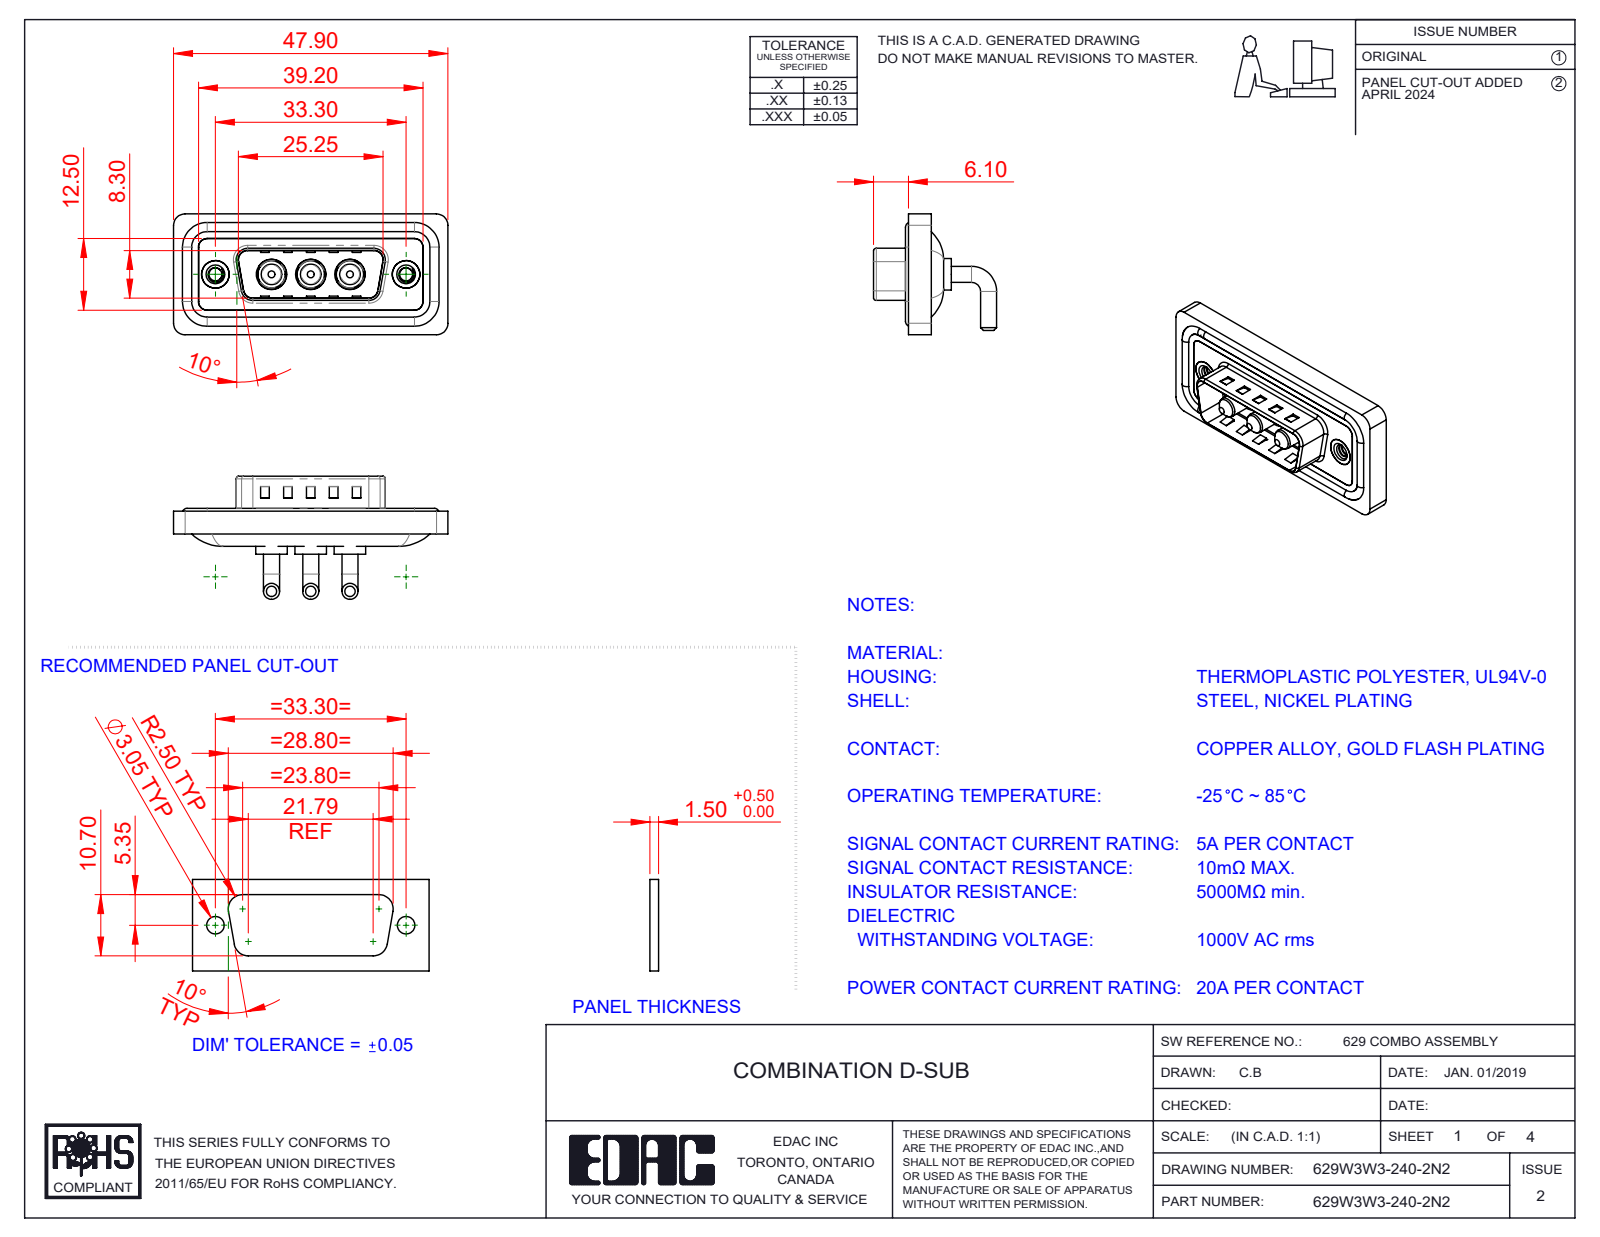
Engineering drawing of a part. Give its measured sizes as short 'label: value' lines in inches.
name: 629Combo Waterproof Housing_15 Contacts; 629Combo Shell Rear_15 Contacts; 629Combo Threaded Rivet_2; Power Pin_20A RA (+3 more)
written by: SolidWorks 2023 (CONFIG_CONTROL_DESIGN)
unit: in
bodies: 13 solids, 576 faces (207 planar, 247 cylindrical, 122 other)
size: 1.886 × 0.846 × 0.831
volume: 0.353 in³; area: 14.01 in²
holes: 3× ⌀0.191, 3× ⌀0.209, 2× ⌀0.089, 2× ⌀0.157, 2× ⌀0.189, 2× ⌀0.197
bosses: 6× ⌀0.11, 4× ⌀0.063, 3× ⌀0.217, 3× ⌀0.205, 3× ⌀0.187, 3× ⌀0.148, 3× ⌀0.142, 2× ⌀0.193
rounds: 20× R0.079, 18× R0.059, 8× R0.02, 8× R0.063, 4× R0.01, 4× R0.024, 4× R0.026, 4× R0.035
face distances: 0.016, 0.114, 0.031, 0.043, 0.083, 0.063, 0.122, 0.098, 0.177, 0.146
hole spacings: 0.27, 0.386, 0.656, 0.925, 0.539, 1.311
